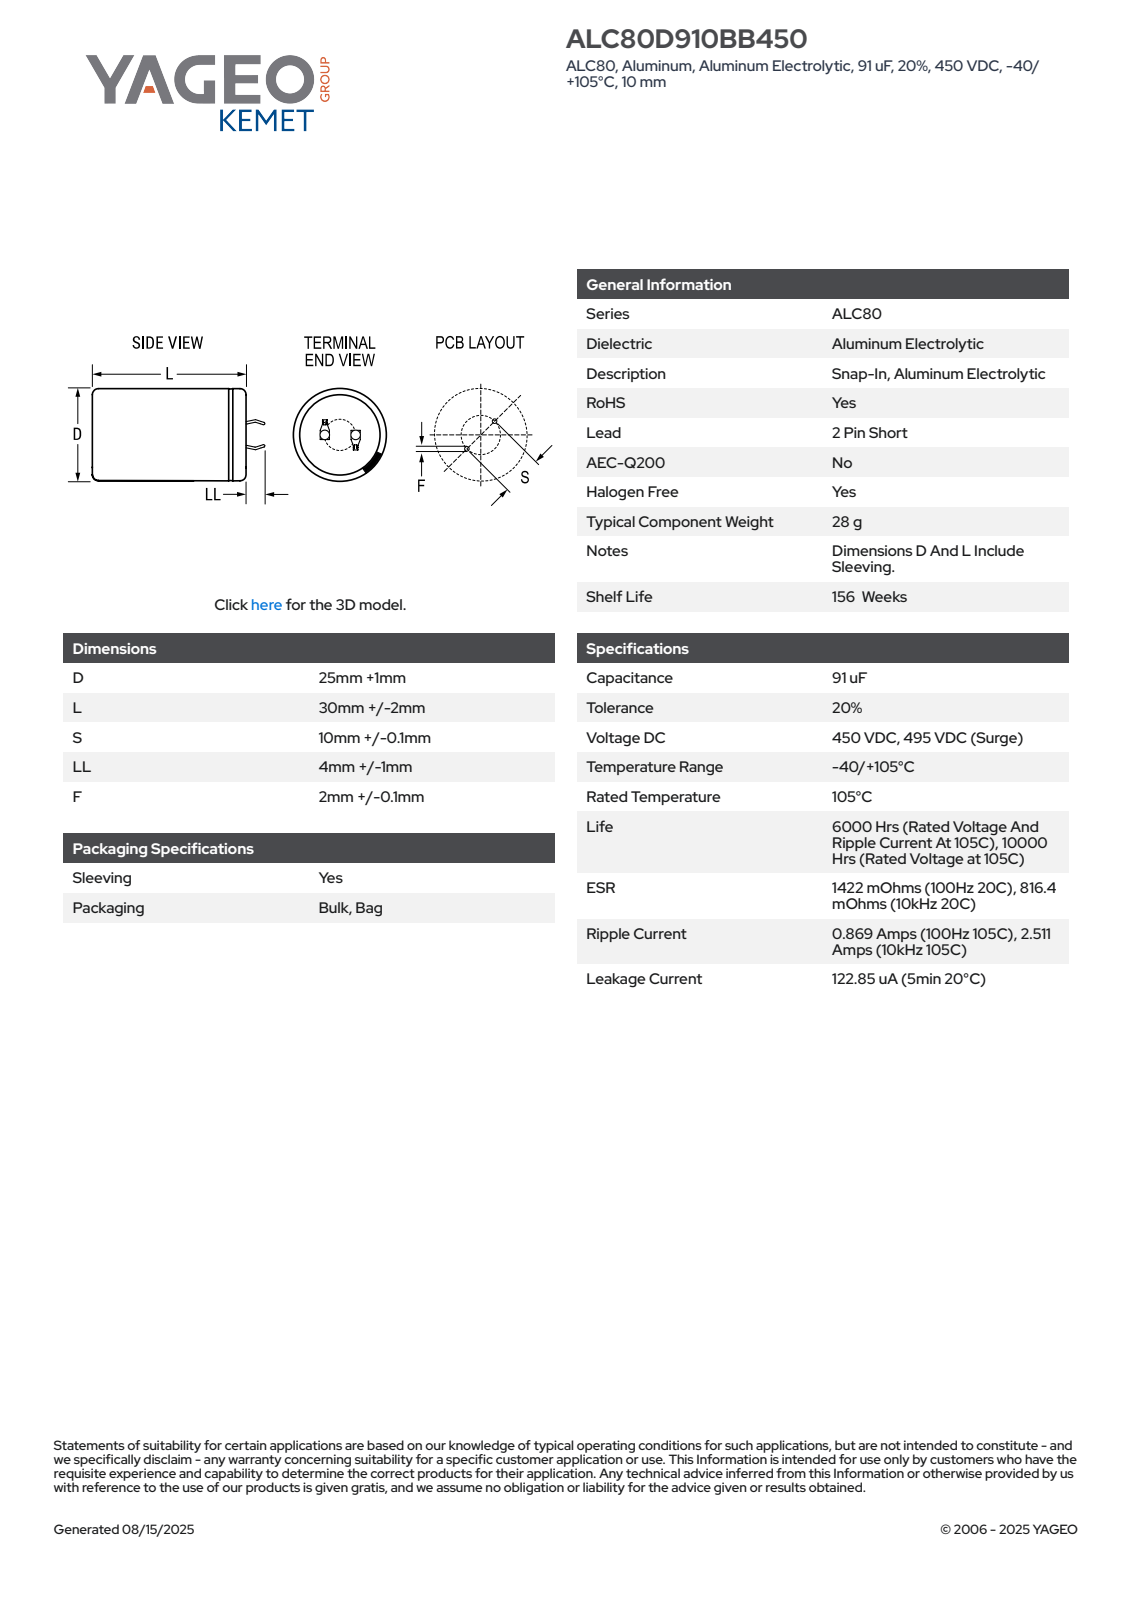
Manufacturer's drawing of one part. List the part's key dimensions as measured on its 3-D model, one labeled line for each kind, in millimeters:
Part name (STEP PRODUCT): CARS_K2P_25X30_D26L32S10LL5F2.1
STEP written by: SolidWorks 2014 (AUTOMOTIVE_DESIGN)
Units: millimetres
Bodies: 1 solid, 100 faces (52 planar, 9 cylindrical, 39 other)
Overall size (bounding box): 36.99 × 26 × 26
Volume: 16 796 mm³ · Surface area: 3 686 mm²
Round holes (diameter × count): ⌀23 ×1
Round bosses / shafts (diameter × count): ⌀26 ×1
Partial cylindrical surfaces — rounded edges, fillets, slot ends (radius × count): R12.99 ×1
Main face-to-face distances: 31.99, 32.49, 0.5, 7.08, 0.6, 0.59, 7.6, 0.75, 1.35, 7.68
